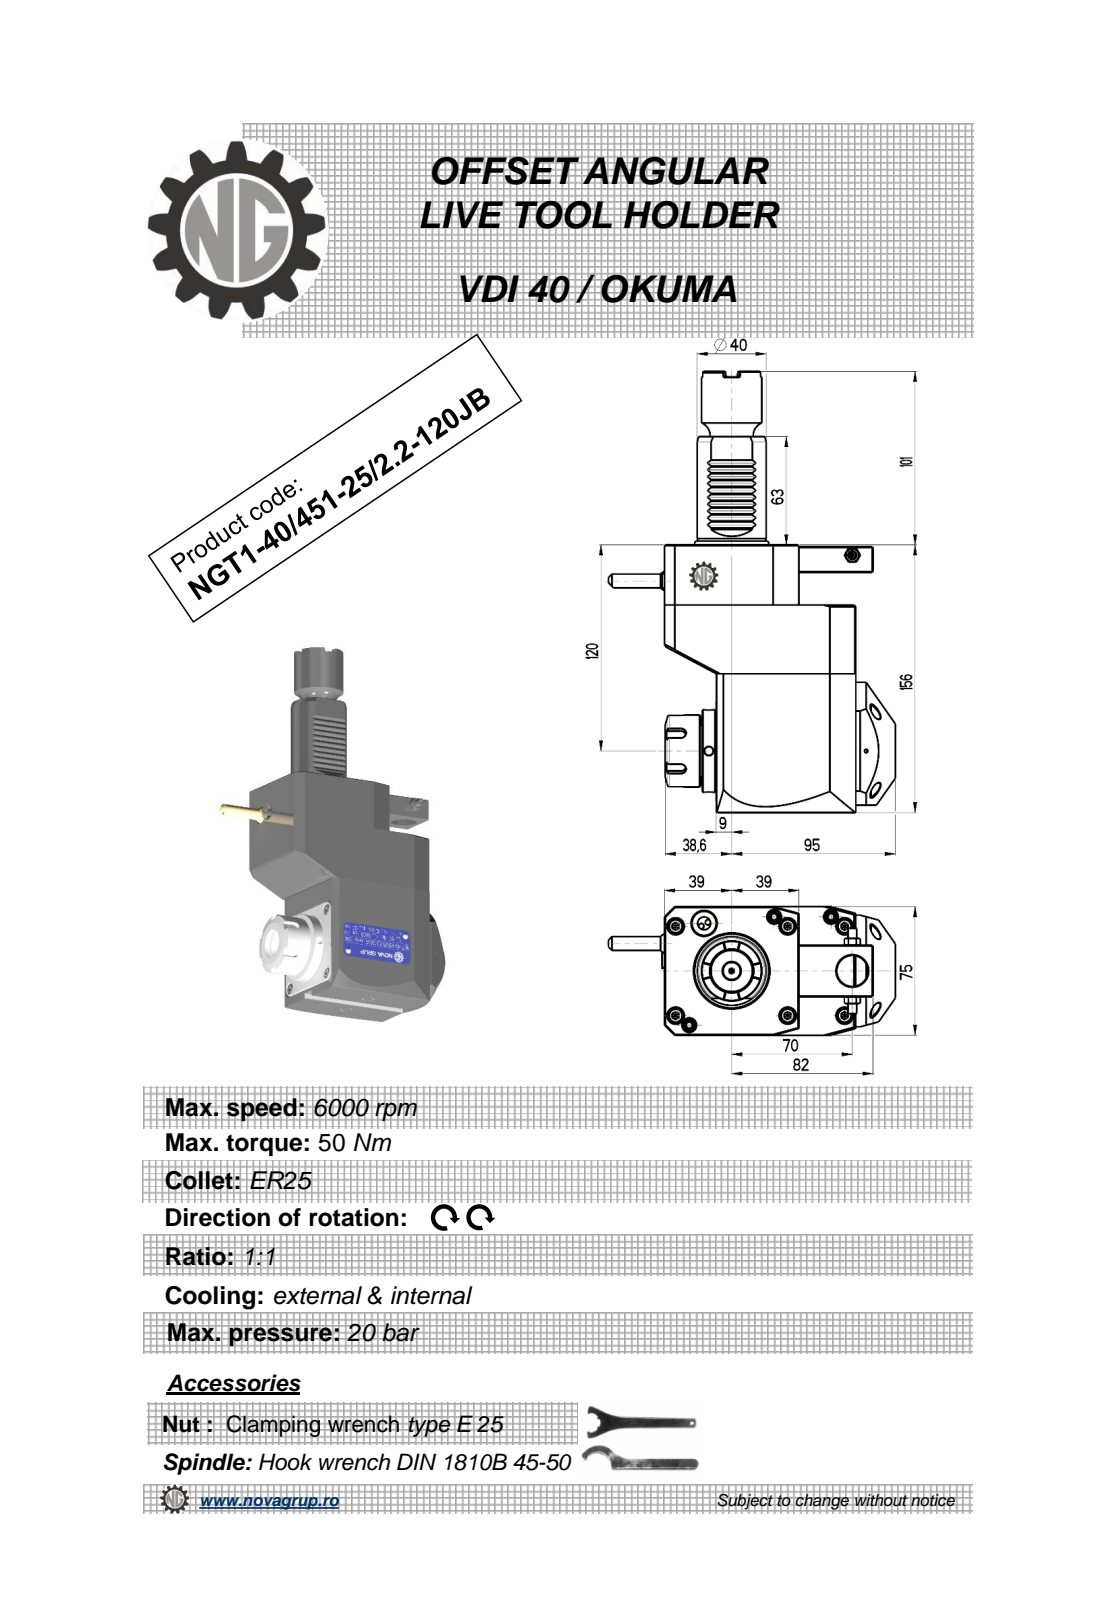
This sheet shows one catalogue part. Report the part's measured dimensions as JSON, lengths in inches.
{"part_name": "NGT1_40_451_25_2_2_120JB", "step_written_by": "PRO/ENGINEER BY PARAMETRIC TECHNOLOGY CORPORATION, 2010280 (CONFIG_CONTROL_DESIGN)", "units": "inches", "bodies": {"solids": 1, "faces": 500, "planar": 218, "cylindrical": 95, "other": 187}, "overall_size": [10.118, 6.555, 3.016], "volume_in3": 74.57, "surface_area_in2": 145.7, "round_holes": [[0.197, 3], [0.118, 1], [0.165, 1], [0.374, 1], [0.709, 1], [0.799, 1], [0.984, 1], [1.055, 1]], "round_bosses_or_shafts": [[1.89, 1], [1.654, 1], [1.575, 1], [1.476, 1], [1.378, 1], [1.299, 1], [1.046, 1], [0.394, 1]], "partial_cylinders_radius": [[0.01, 12], [0.012, 10], [0.008, 6], [0.118, 5], [0.02, 1], [1.575, 1]], "face_to_face_distances": [2.953, 6.142, 4.37, 1.181, 4.764, 1.378, 3.189, 1.299, 3.071, 1.89], "hole_center_spacings": [0.522, 0.824, 2.756, 3.278, 3.948, 4.429, 5.557]}
